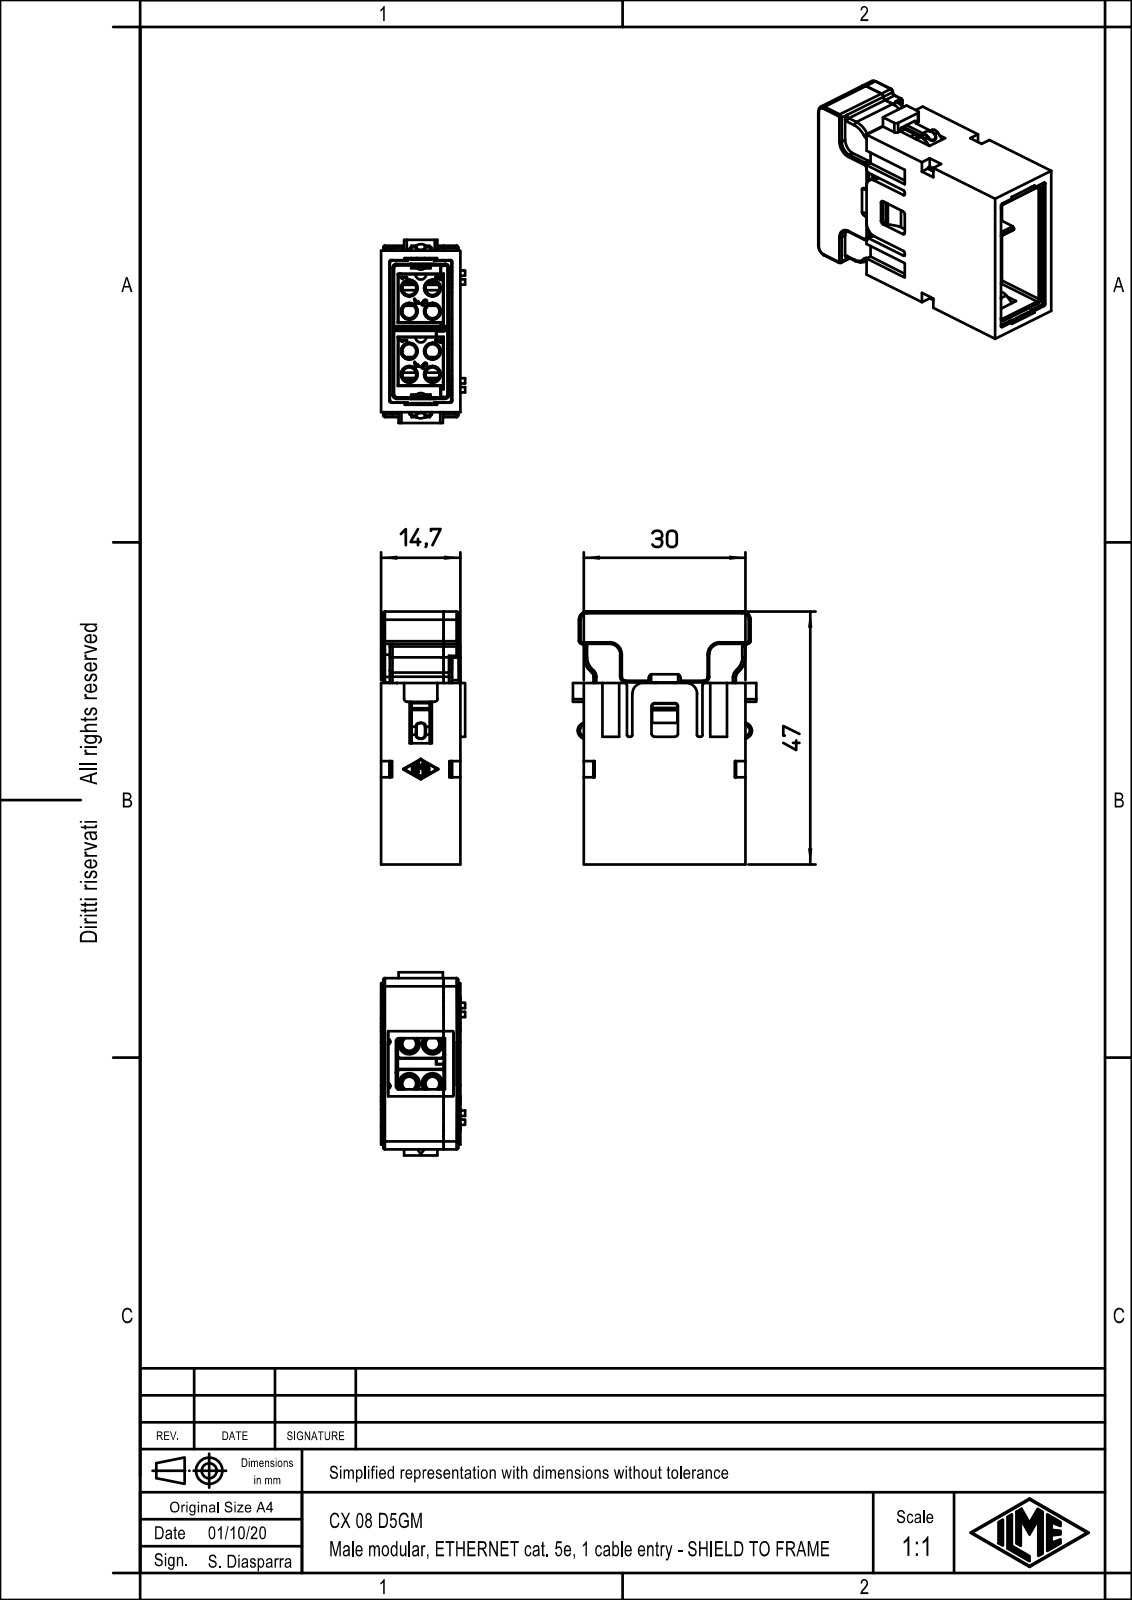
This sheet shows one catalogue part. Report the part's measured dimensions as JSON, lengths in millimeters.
{"part_name": "CX 08 D5GM", "step_written_by": "Creo Elements/Direct Modeling 20.1B 02-Apr-2019 (C) Parametric Technology GmbH (AUTOMOTIVE_DESIGN)", "units": "millimeters", "bodies": {"solids": 1, "faces": 682, "planar": 398, "cylindrical": 215, "other": 69}, "overall_size": [46.95, 34, 15.6], "volume_mm3": 15895, "surface_area_mm2": 12626, "round_holes": [[2.6, 10], [2.25, 2], [5, 2], [1.4, 1]], "round_bosses_or_shafts": [[4.7, 2], [1.9, 2], [1.3, 1]], "partial_cylinders_radius": [[0.5, 50], [0.3, 40], [1, 10], [0.4, 8], [0.65, 8], [2, 6], [0.1, 4], [0.2, 4]], "face_to_face_distances": [1.6, 13.1, 1.55, 13.15, 11.55, 11.5, 11.6, 14.7, 0.4, 1.15], "hole_center_spacings": [4.3, 6.08, 11.7, 12.47, 7.4, 8.56, 16, 16.57]}
